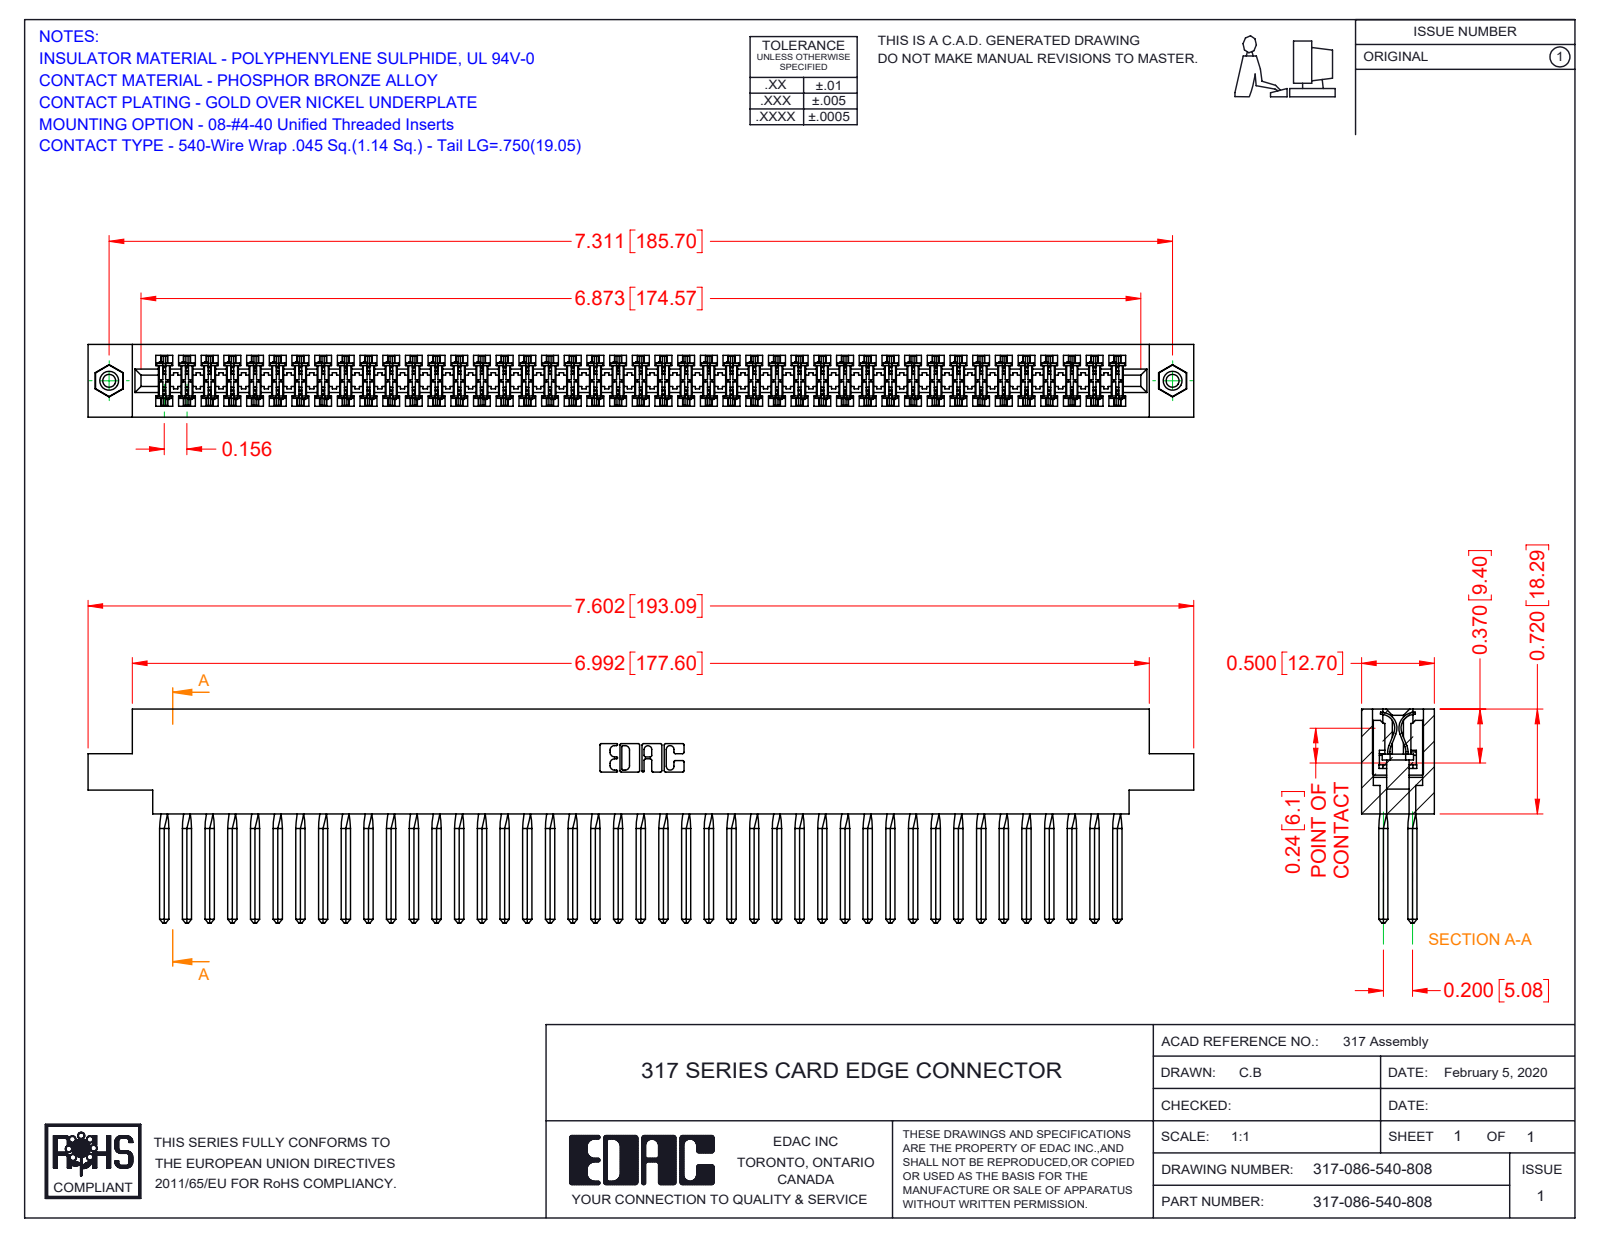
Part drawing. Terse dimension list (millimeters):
name: 317-086-540-808; 317 Part_.156 Dia - TI; 317-290-001_540; 345-250-001_345-250-003-102
written by: SolidWorks 2016 (CONFIG_CONTROL_DESIGN)
unit: mm
bodies: 89 solids, 7816 faces (6368 planar, 1088 cylindrical, 360 other)
size: 193.1 × 37.3 × 12.7
volume: 32 430 mm³; area: 48 420 mm²
holes: 2× ⌀2.3, 2× ⌀3.2, 2× ⌀4
bosses: 2× ⌀3.9
rounds: 172× R0.4, 22× R0.3, 6× R0.2, 6× R0.8, 3× R0.7, 2× R2.4, 2× R2.5, 2× R2.8
face distances: 12.7, 1.9, 10.8, 8.9, 5, 2.4, 5.1, 2.9, 3.3, 1.2
hole spacings: 185.7
